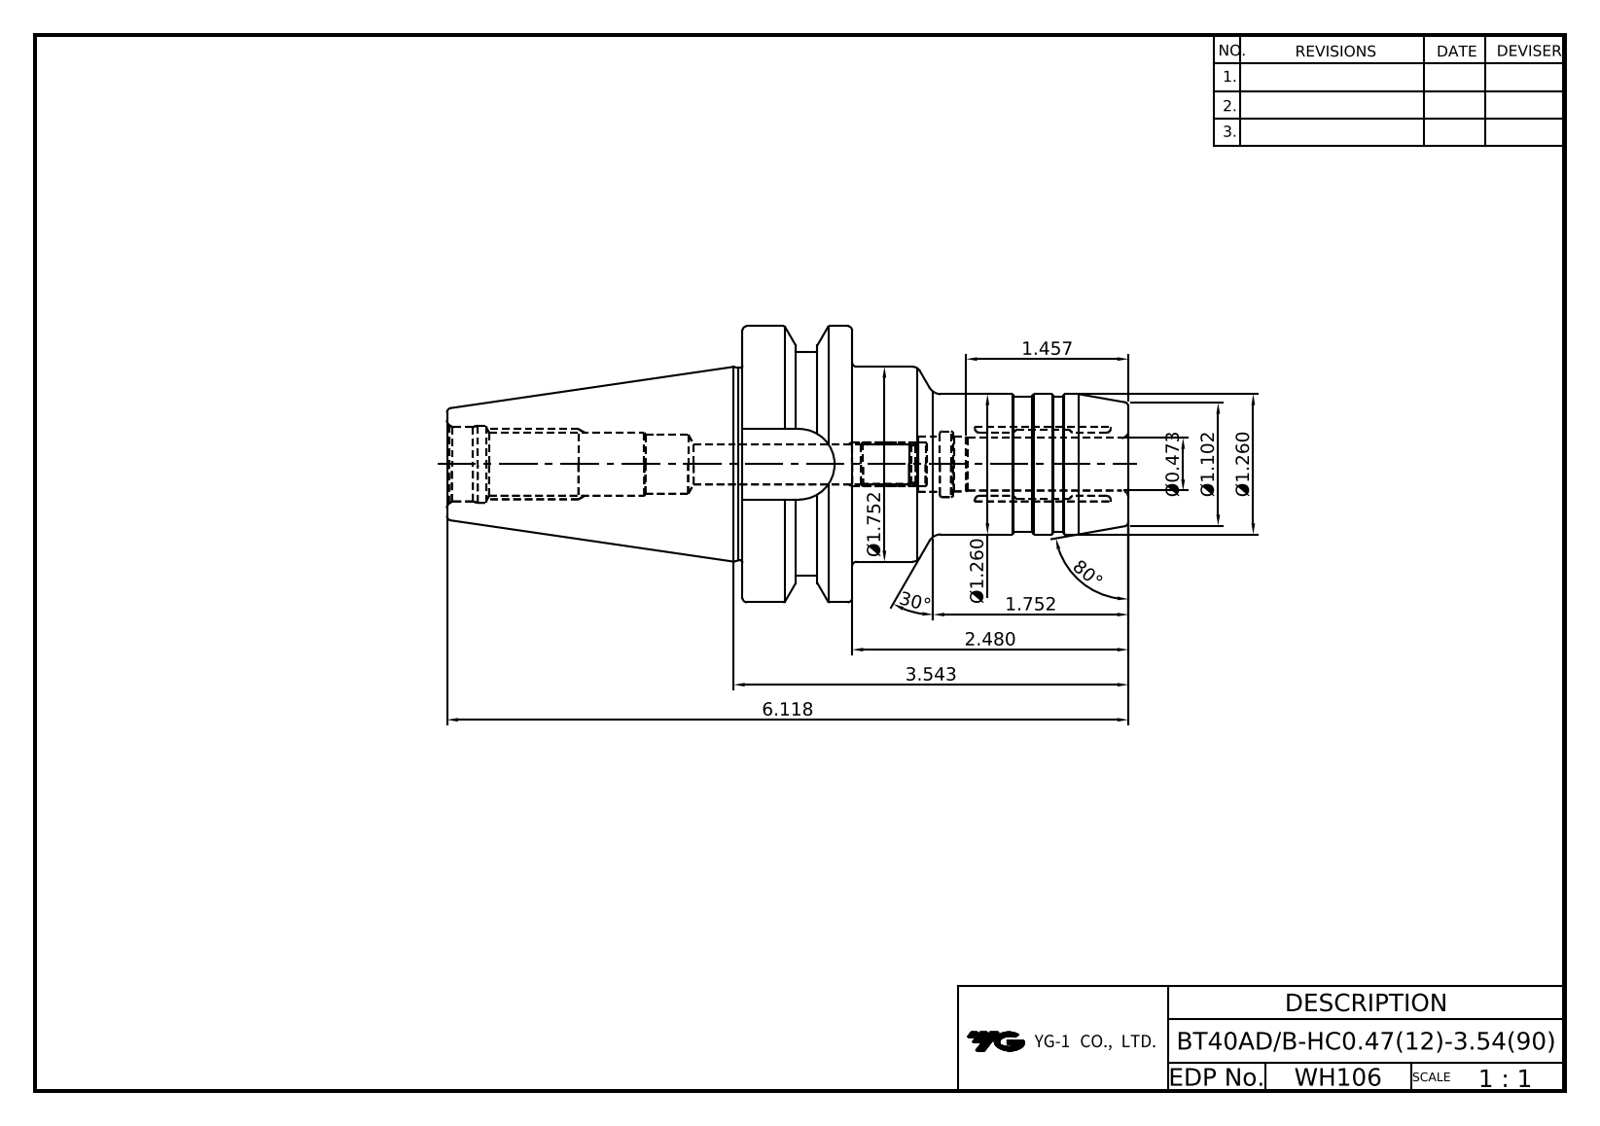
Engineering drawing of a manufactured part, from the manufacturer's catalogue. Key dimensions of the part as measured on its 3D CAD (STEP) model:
Part name (STEP PRODUCT): LO-BT40ADB-HC12-90
STEP written by: Autodesk Inventor 2022 (AUTOMOTIVE_DESIGN)
Units: millimetres
Bodies: 1 solid, 88 faces (21 planar, 33 cylindrical, 34 other)
Overall size (bounding box): 155.4 × 63 × 63
Volume: 176 833 mm³ · Surface area: 31 590 mm²
Round holes (diameter × count): ⌀3.24 ×4, ⌀4 ×4, ⌀8.92 ×1, ⌀12 ×1, ⌀12.6 ×1, ⌀13.5 ×1, ⌀13.84 ×1, ⌀17 ×1, ⌀17.6 ×1
Round bosses / shafts (diameter × count): ⌀63 ×1, ⌀51 ×1, ⌀44.5 ×1, ⌀44 ×1, ⌀32 ×1, ⌀31 ×1
Partial cylindrical surfaces — rounded edges, fillets, slot ends (radius × count): R8.05 ×1
Main face-to-face distances: 25, 88, 63, 45.2, 5, 17.1, 7.9, 70.9, 12.1, 12.9
